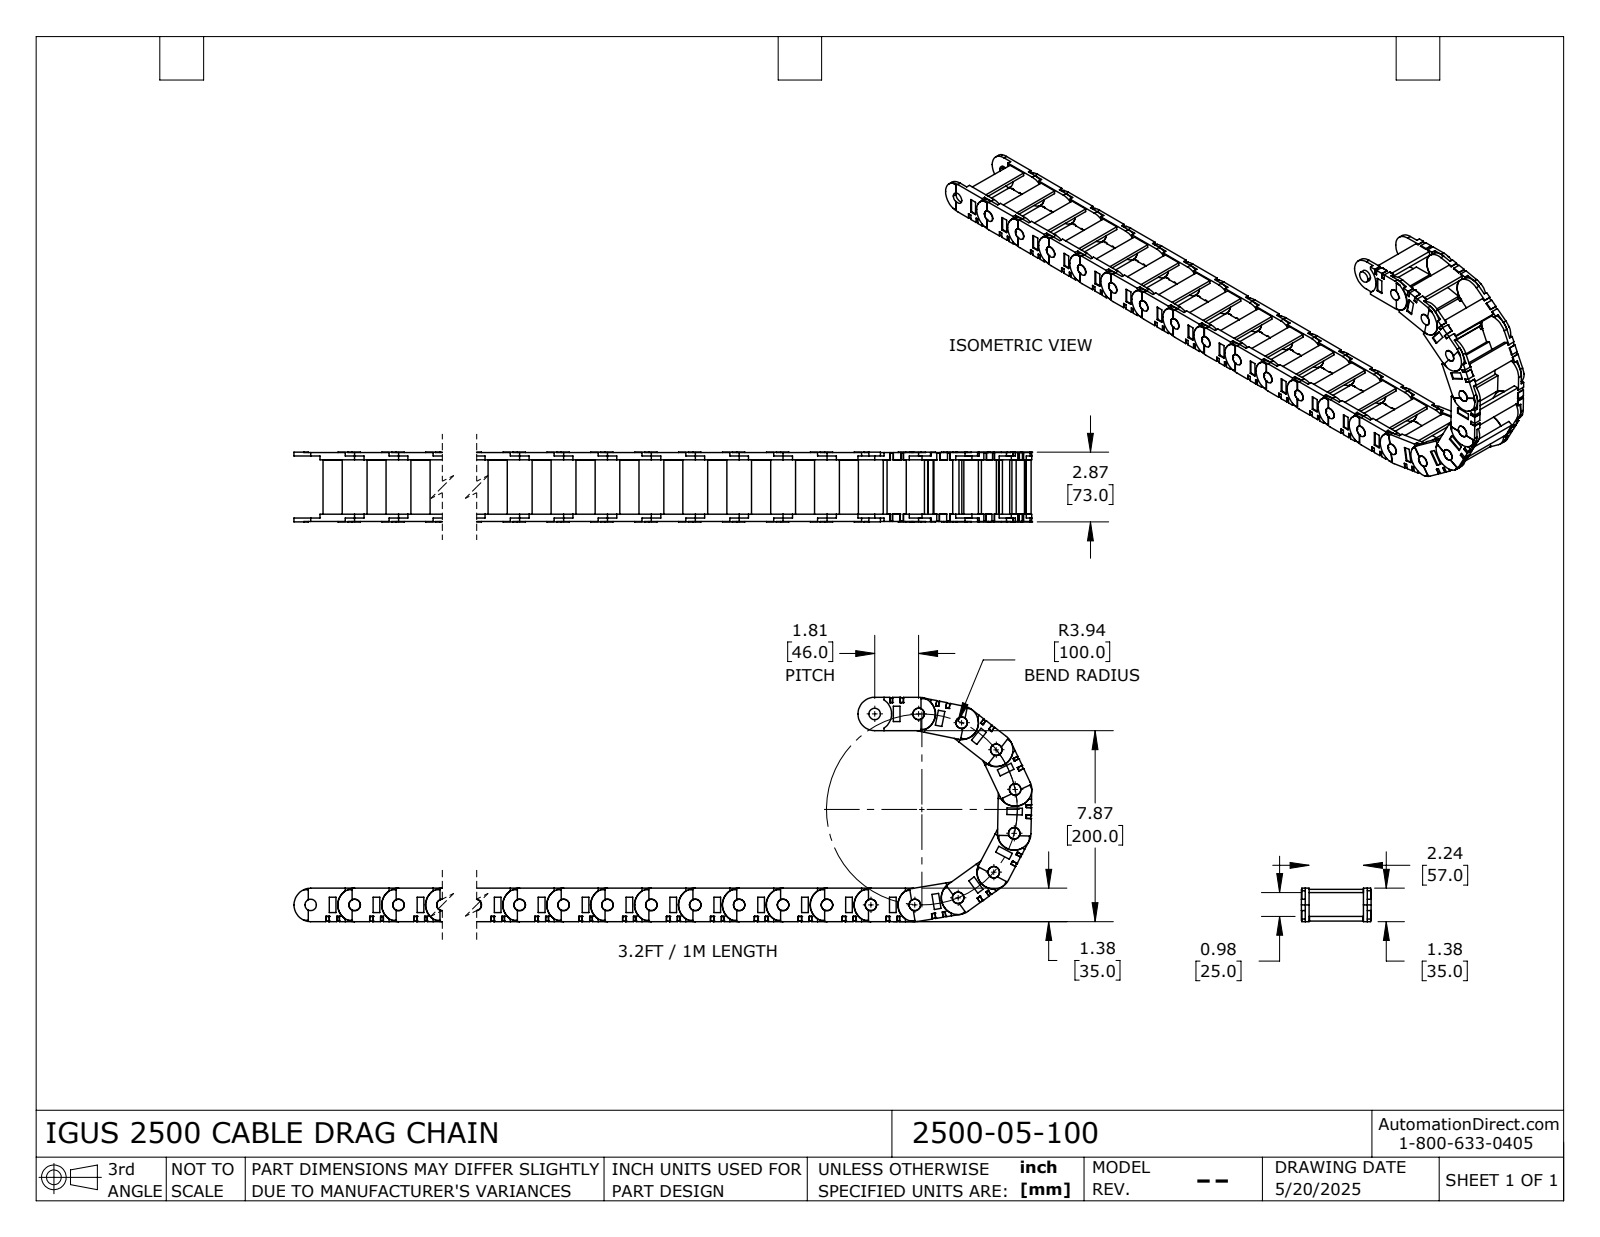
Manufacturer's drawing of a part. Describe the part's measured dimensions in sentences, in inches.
The part is named "2500_05_100". Its 3-D file was written by "SolidWorks 2024 (AUTOMOTIVE_DESIGN)". It is 66 solids with 2398 faces: 1870 planar, 528 cylindrical and 0 other. Overall it measures 30.87 by 9.252 by 2.874 inches. Its volume is 45.18 cubic inches and its surface area 663.9 square inches. Round holes: 22 of diameter 0.473. Round bosses or shafts: 22 of diameter 0.472, 21 of diameter 1.378. Partial cylindrical surfaces (rounded edges, fillets, slot ends): 23 of radius 0.697, 2 of radius 0.689. The main face-to-face distances are 0.157, 2.402, 2.559, 0.142, 0.299, 2.543, 2.701, 2.244, 0.134, 0.197. The hole center spacings are 1.811, 3.622, 5.433, 7.244, 9.055, 10.866, 12.677, 14.488.
